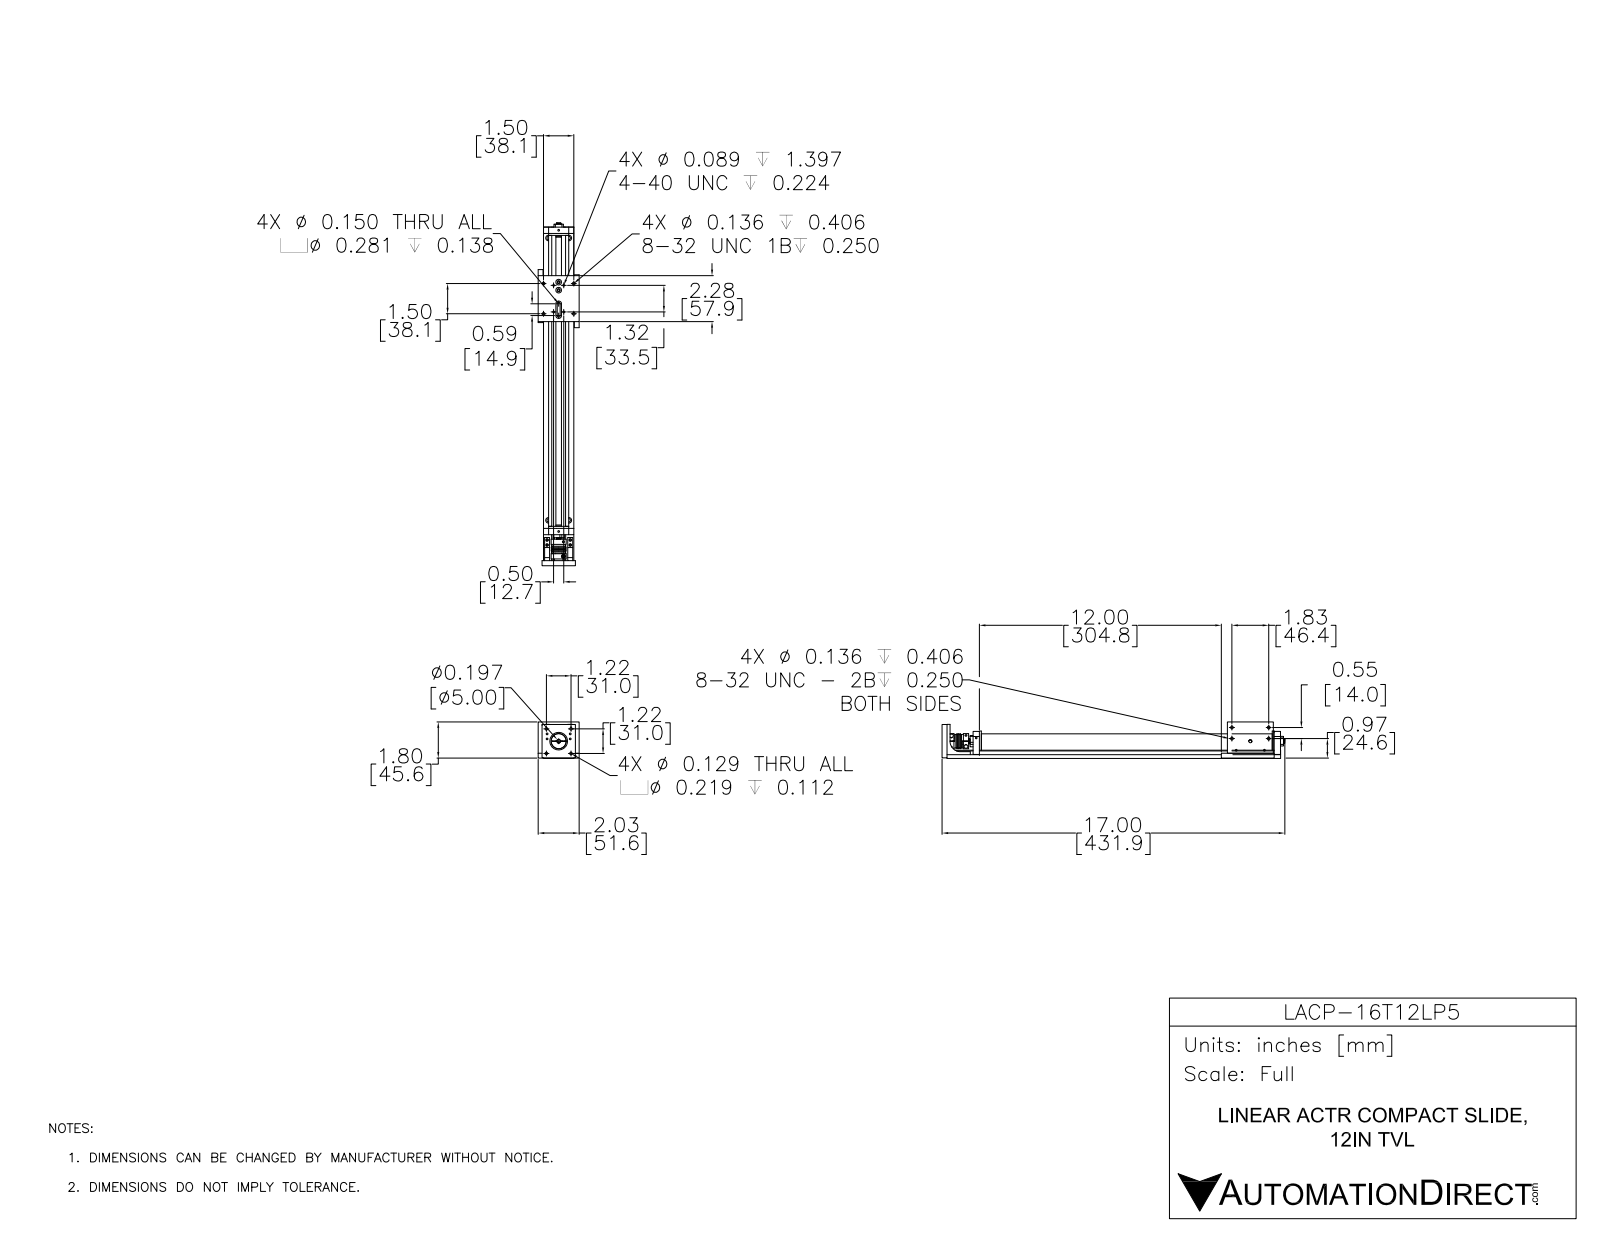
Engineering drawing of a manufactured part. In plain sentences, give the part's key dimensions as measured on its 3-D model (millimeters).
The part is named "LACP-16T12LP5; LACP-16TXXLP5-CAR; LACP-16T12LP5-RAIL". Its 3-D file was written by "SolidWorks 2016 (AUTOMOTIVE_DESIGN)". It is 25 solids with 827 faces: 271 planar, 472 cylindrical and 84 other. Overall it measures 431.7 by 51.6 by 46 millimeters. Its volume is 343 500 cubic millimeters and its surface area 154 600 square millimeters. Round holes: 16 of diameter 2.3, 10 of diameter 7.1, 8 of diameter 3.5, 8 of diameter 4.3, 6 of diameter 3.8, 4 of diameter 1.8, 4 of diameter 3.3, 4 of diameter 3.3, 4 of diameter 3.5, 4 of diameter 5.6, 4 of diameter 7.1, 3 of diameter 5. Round bosses or shafts: 3 of diameter 4, 2 of diameter 3.8, 1 of diameter 25.4, 1 of diameter 19, 1 of diameter 18, 1 of diameter 17.1, 1 of diameter 17, 1 of diameter 15. Partial cylindrical surfaces (rounded edges, fillets, slot ends): 4 of radius 1.2, 4 of radius 1.6, 4 of radius 2.4, 3 of radius 3.2, 2 of radius 1.3, 2 of radius 1.9, 2 of radius 3.6, 2 of radius 6.4. The main face-to-face distances are 4.7, 6.7, 44.8, 31, 26.2, 6.4, 41.2, 46, 15.1, 51.6. The hole center spacings are 102.4, 12.7, 101.6, 203.6, 104.7, 203.2, 6.4, 8.1.
